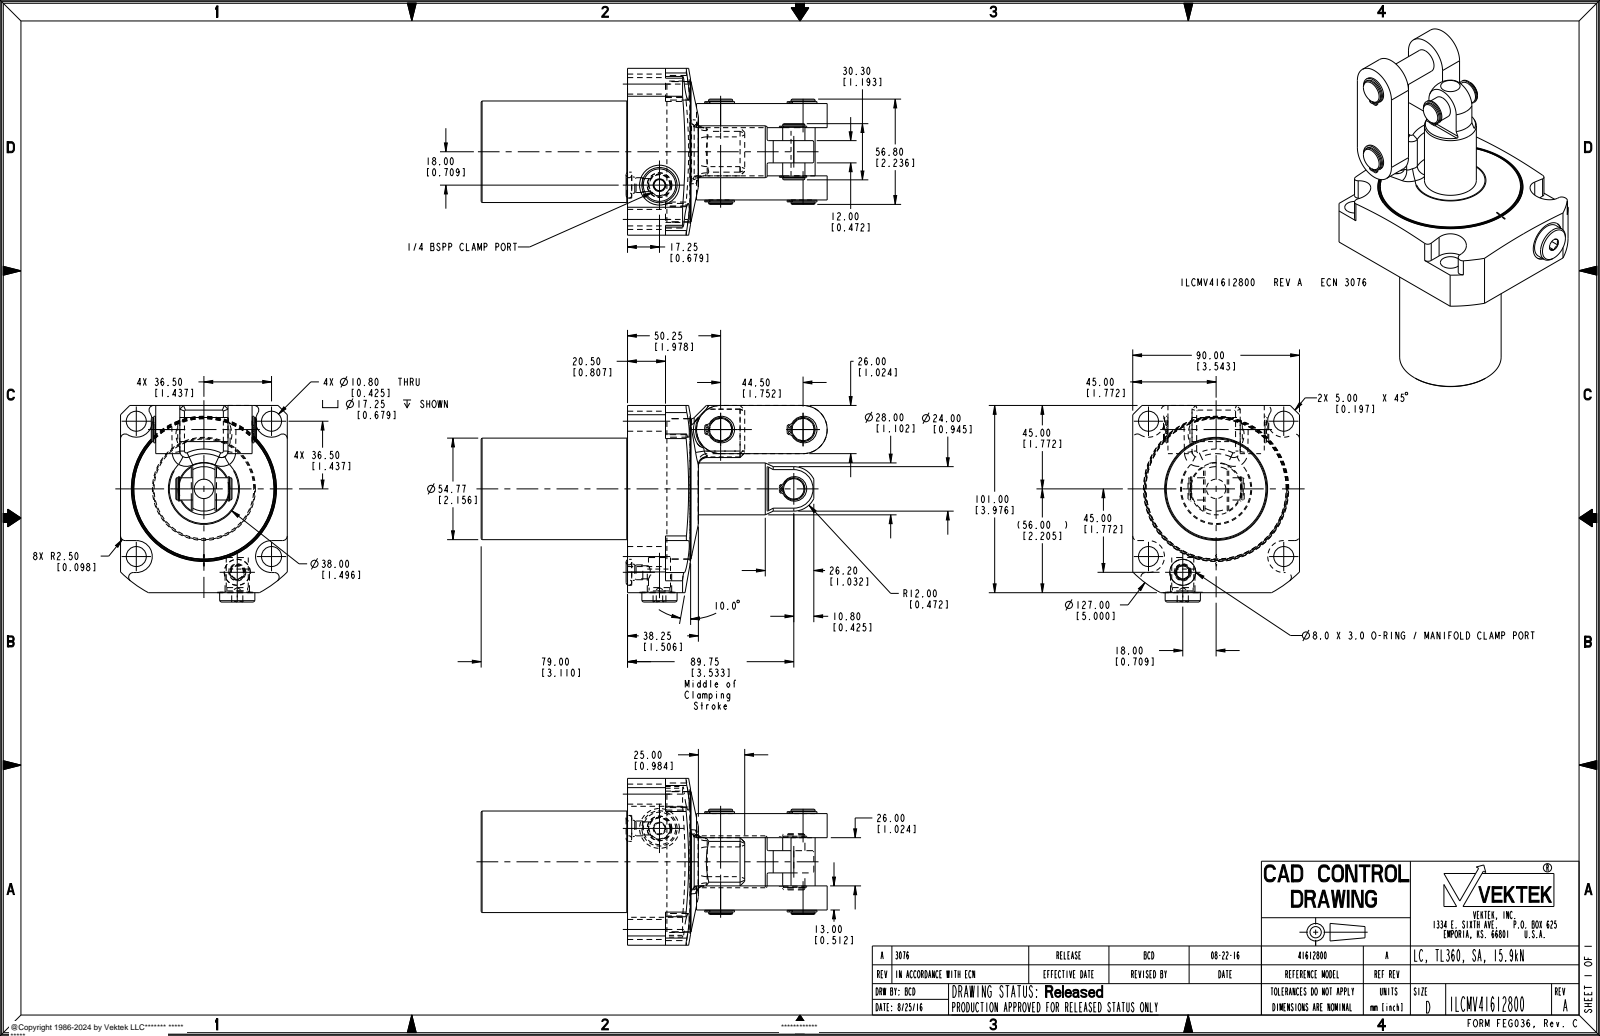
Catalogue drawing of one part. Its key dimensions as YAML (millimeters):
part_name: "ILCMV41612800_BODY; ILCMV41612800_LUG; ILCMV41612800"
step_written_by: "PRO/ENGINEER BY PARAMETRIC TECHNOLOGY CORPORATION, 2013320 (AUTOMOTIVE_DESIGN)"
units: millimeters
bodies: {solids: 3, faces: 345, planar: 120, cylindrical: 153, other: 72}
overall_size: [186.75, 106.06, 90]
volume: 571974
surface_area: 82666
round_holes:
  - {diameter: 1.19, count: 4}
  - {diameter: 10.8, count: 4}
  - {diameter: 1.04, count: 2}
  - {diameter: 7.04, count: 1}
  - {diameter: 11.89, count: 1}
  - {diameter: 14, count: 1}
  - {diameter: 21.5, count: 1}
  - {diameter: 75.79, count: 1}
round_bosses_or_shafts:
  - {diameter: 14.33, count: 2}
  - {diameter: 13, count: 2}
  - {diameter: 11.89, count: 2}
  - {diameter: 75.68, count: 1}
  - {diameter: 54.77, count: 1}
  - {diameter: 28, count: 1}
  - {diameter: 19, count: 1}
  - {diameter: 13.24, count: 1}
partial_cylinders:
  - {radius: 2.5, count: 8}
  - {radius: 0.8, count: 4}
  - {radius: 1.19, count: 4}
  - {radius: 1.82, count: 4}
  - {radius: 8.62, count: 4}
  - {radius: 1.04, count: 2}
  - {radius: 1.35, count: 2}
  - {radius: 3.5, count: 2}
face_to_face_distances: [21.25, 19, 32, 39, 71, 90, 79, 100.25, 26, 13]
hole_center_spacings: [51.62, 73, 3.1, 44.5, 44.61, 103.24, 2.6, 20.36]
